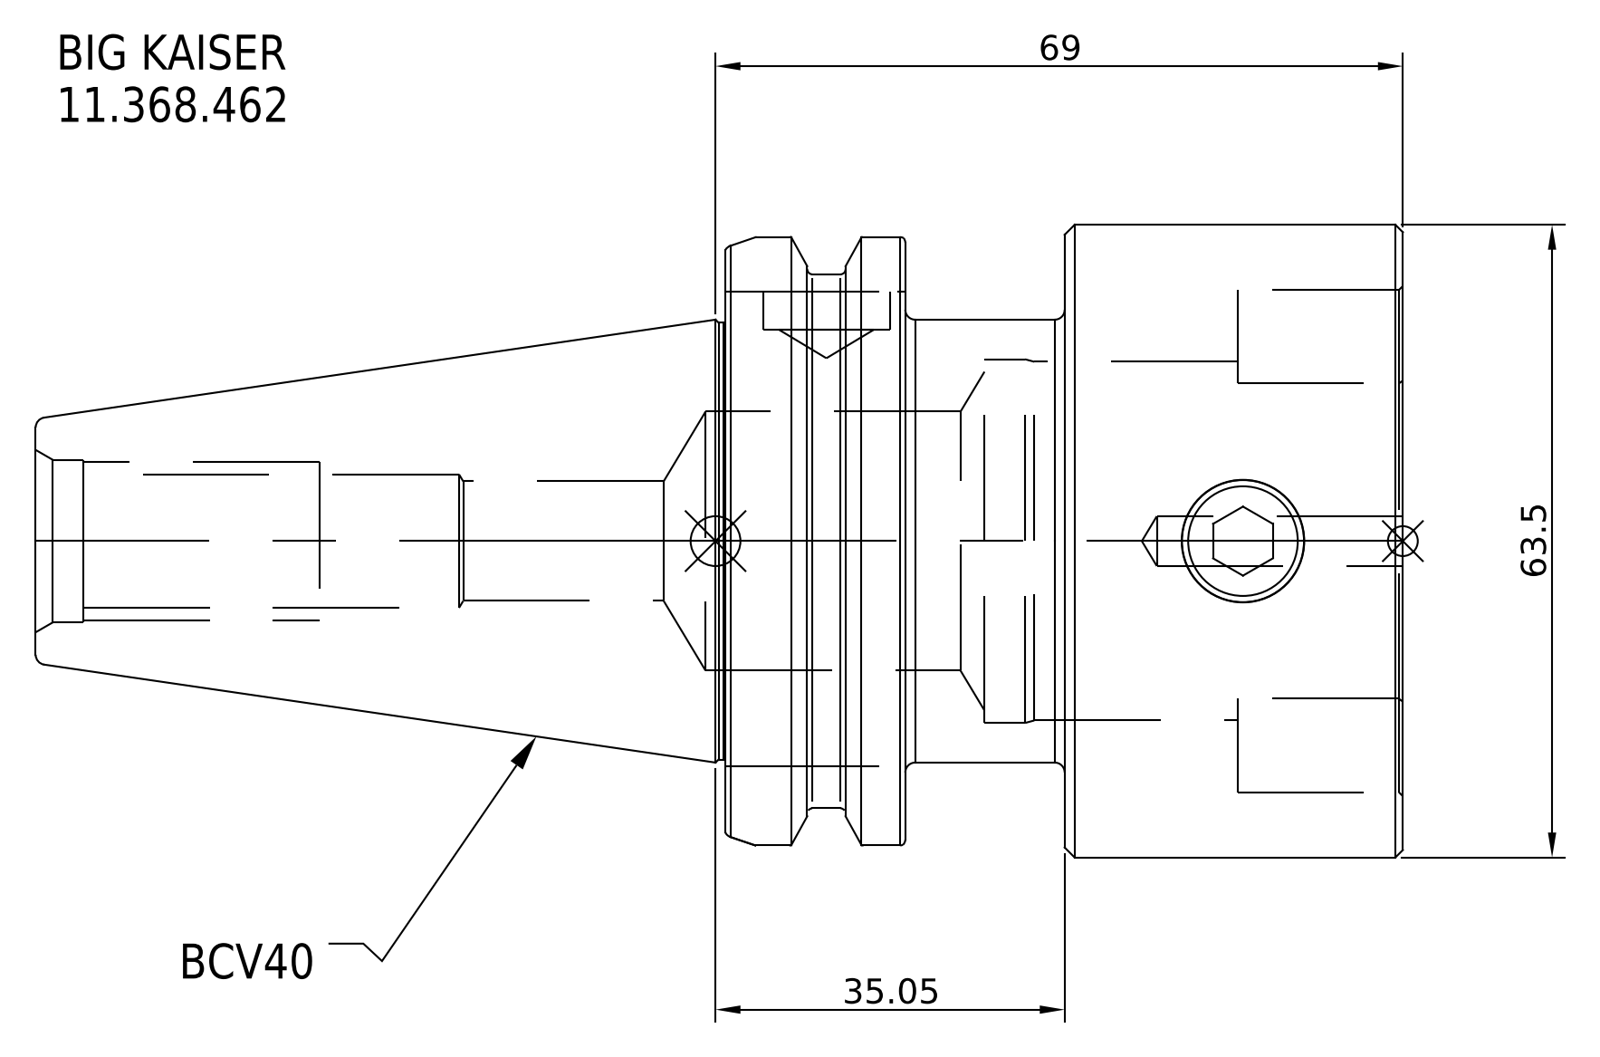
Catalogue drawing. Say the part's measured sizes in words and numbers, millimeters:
The part is named "11.368.462". Its 3-D file was written by "SolidWorks 2021 (CONFIG_CONTROL_DESIGN)". It is 1 solid with 16 faces: 7 planar, 6 cylindrical and 3 other. Overall it measures 137.25 by 63.5 by 63.5 millimeters. Its volume is 248 883 cubic millimeters and its surface area 29 290 square millimeters. Round bosses or shafts: 1 of diameter 63.5, 1 of diameter 63.27, 1 of diameter 56.36, 1 of diameter 44.45. The main face-to-face distances are 65.83, 49.95, 15.88, 33.95, 16, 31.88, 137.25, 103.3, 87.3, 71.42.
